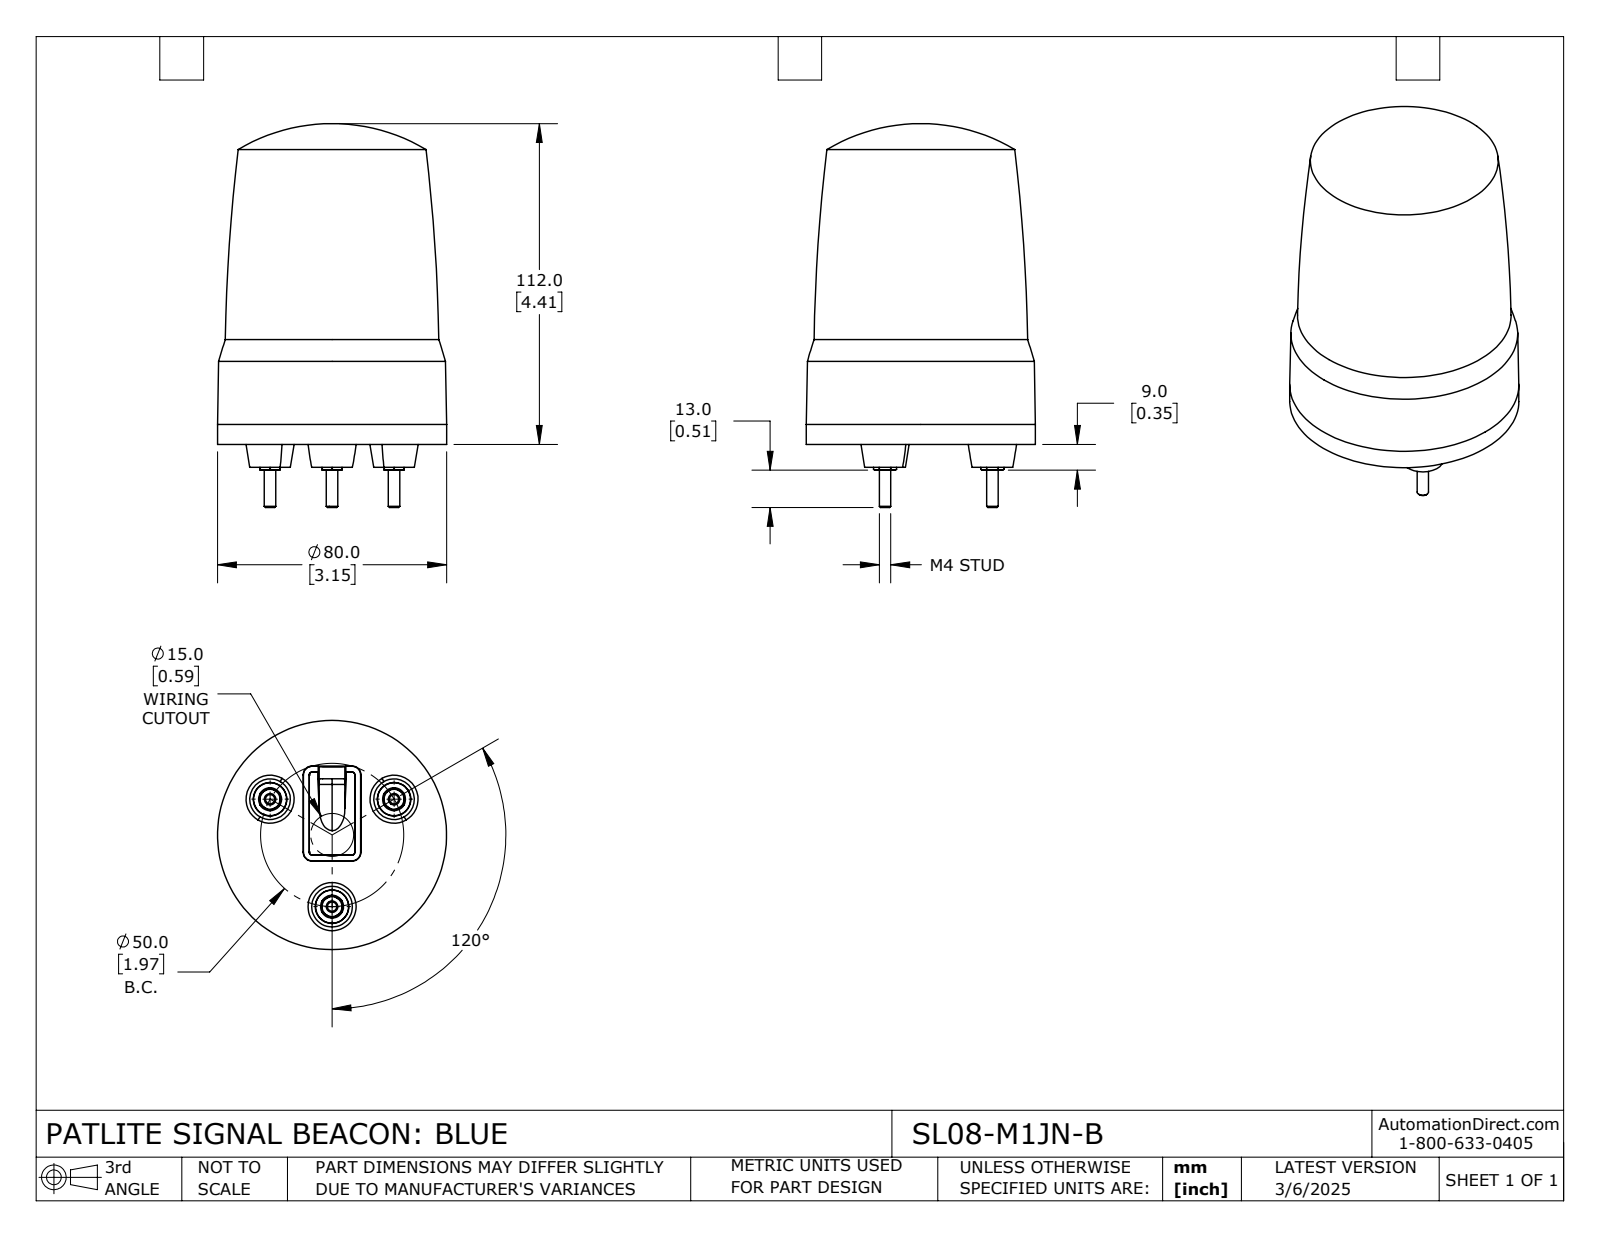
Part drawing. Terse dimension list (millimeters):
name: SL08-M1JN-B
written by: SolidWorks 2024 (CONFIG_CONTROL_DESIGN)
unit: mm
bodies: 1 solid, 138 faces (47 planar, 14 cylindrical, 77 other)
size: 134 × 80 × 80
volume: 463 225 mm³; area: 35 408 mm²
bosses: 3× ⌀8, 3× ⌀4, 1× ⌀80
face distances: 0.85, 2.45, 1.6, 5.3, 6.15, 7.75, 2.7, 8, 8.85, 10.45
